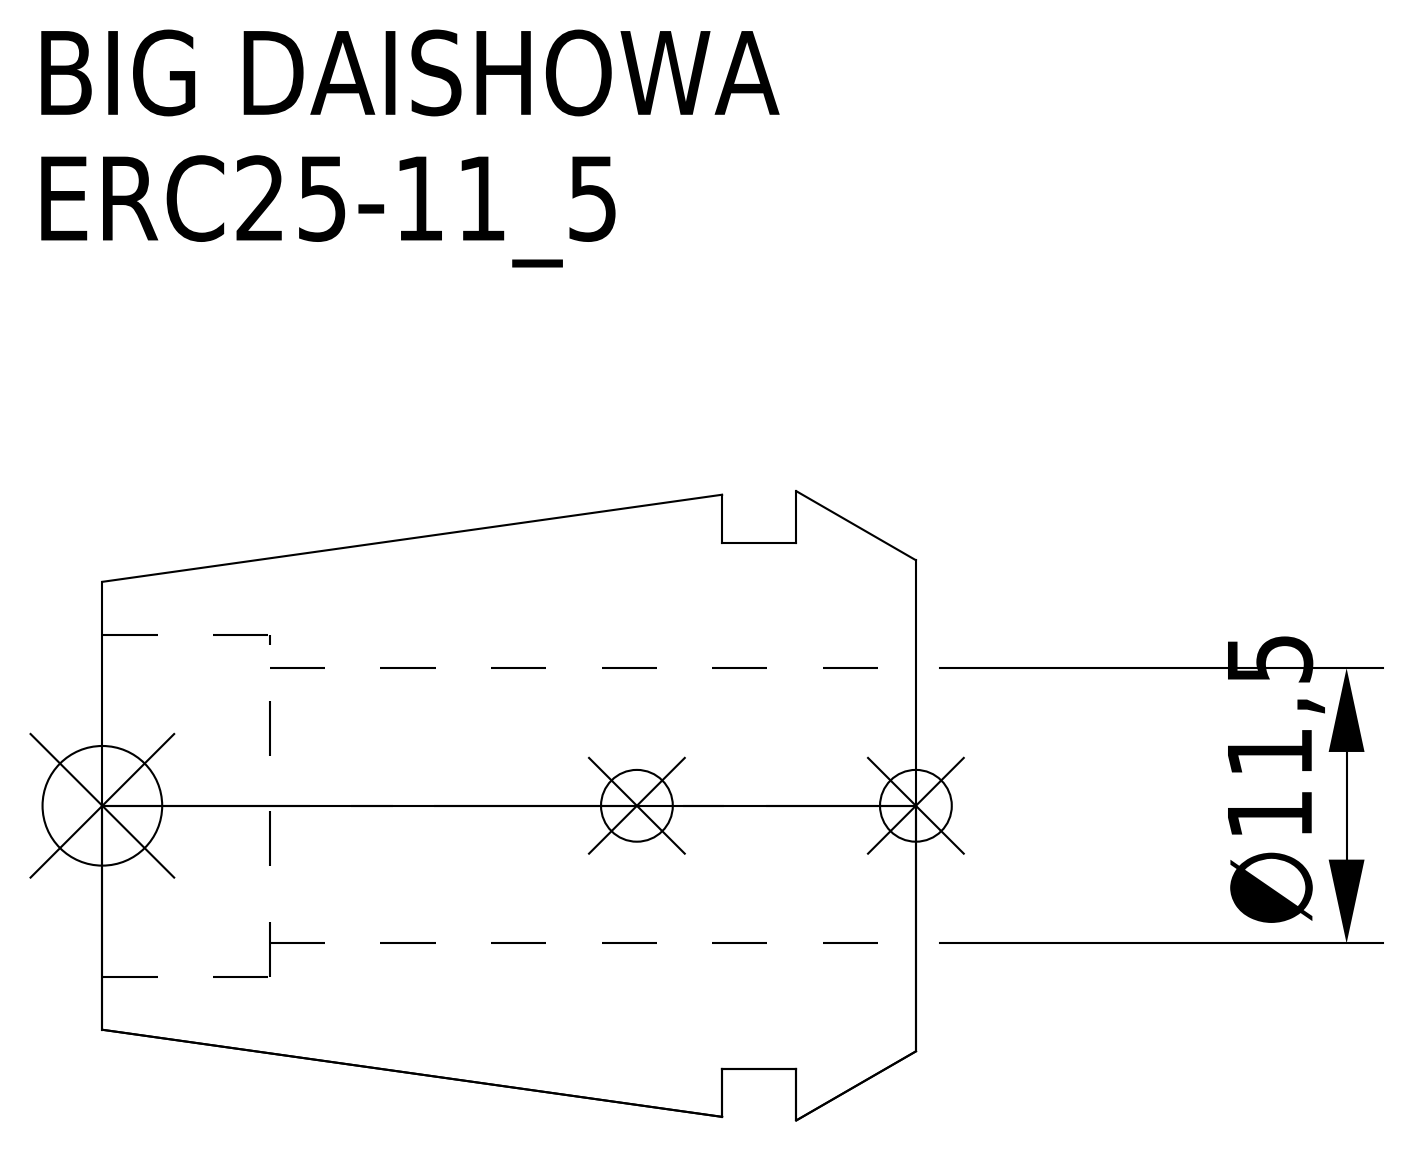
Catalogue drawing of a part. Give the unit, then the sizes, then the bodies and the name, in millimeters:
Units: millimetres
Overall size (bounding box): 34 × 26.3 × 26.3
Round holes (diameter × count): ⌀11.5 ×1, ⌀14.3 ×1
Round bosses / shafts (diameter × count): ⌀22 ×1
Main face-to-face distances: 5, 8.1, 3.1, 34, 29, 25.9, 27, 22, 18.9, 7
Volume: 9 674 mm³ · Surface area: 4 479 mm²
Bodies: 1 solid, 15 faces (5 planar, 6 cylindrical, 4 other)
Part name (STEP PRODUCT): ERC25-11_5
STEP written by: CREO PARAMETRIC BY PTC INC, 2016380 (AUTOMOTIVE_DESIGN)
